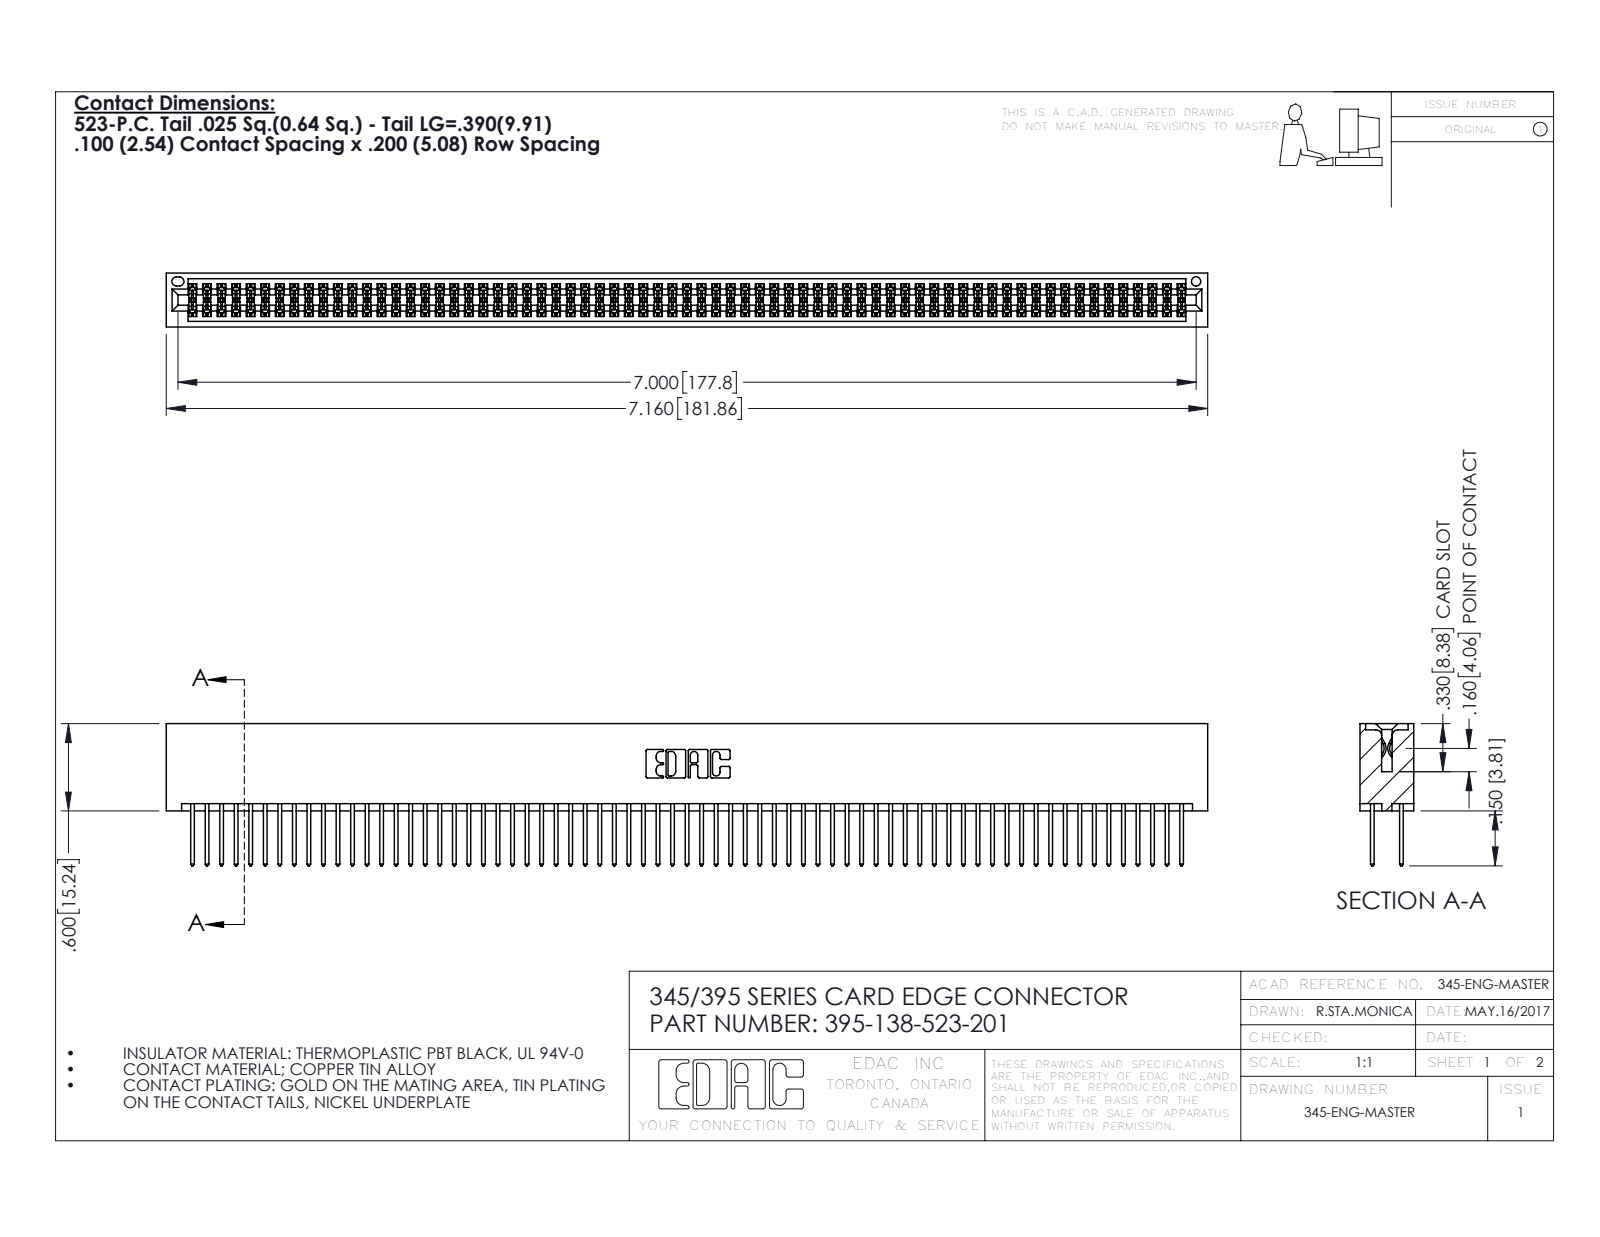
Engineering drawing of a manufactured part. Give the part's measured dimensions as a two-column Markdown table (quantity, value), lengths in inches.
| quantity | value |
| --- | --- |
| part name | 345 Part_No Mounting Lugs; 395-138-523-201; 345-292-001_345-293-123 |
| STEP written by | SolidWorks 2016 (CONFIG_CONTROL_DESIGN) |
| units | inches |
| bodies | 139 solids, 7018 faces (4630 planar, 2388 cylindrical, 0 other) |
| overall size | 7.16 × 0.977 × 0.37 |
| volume | 1.148 in³ |
| surface area | 46.36 in² |
| round holes (diameter × count) | 0.064 × 1 |
| partial cylindrical surfaces (radius × count) | 0.006 × 207, 0.01 × 138, 0.01 × 22, 0.007 × 6, 0.031 × 6, 0.026 × 3, 0.014 × 2, 0.019 × 2 |
| main face-to-face distances | 0.298, 0.072, 0.2, 0.098, 0.272, 0.025, 0.37, 0.225, 0.175, 0.149 |
